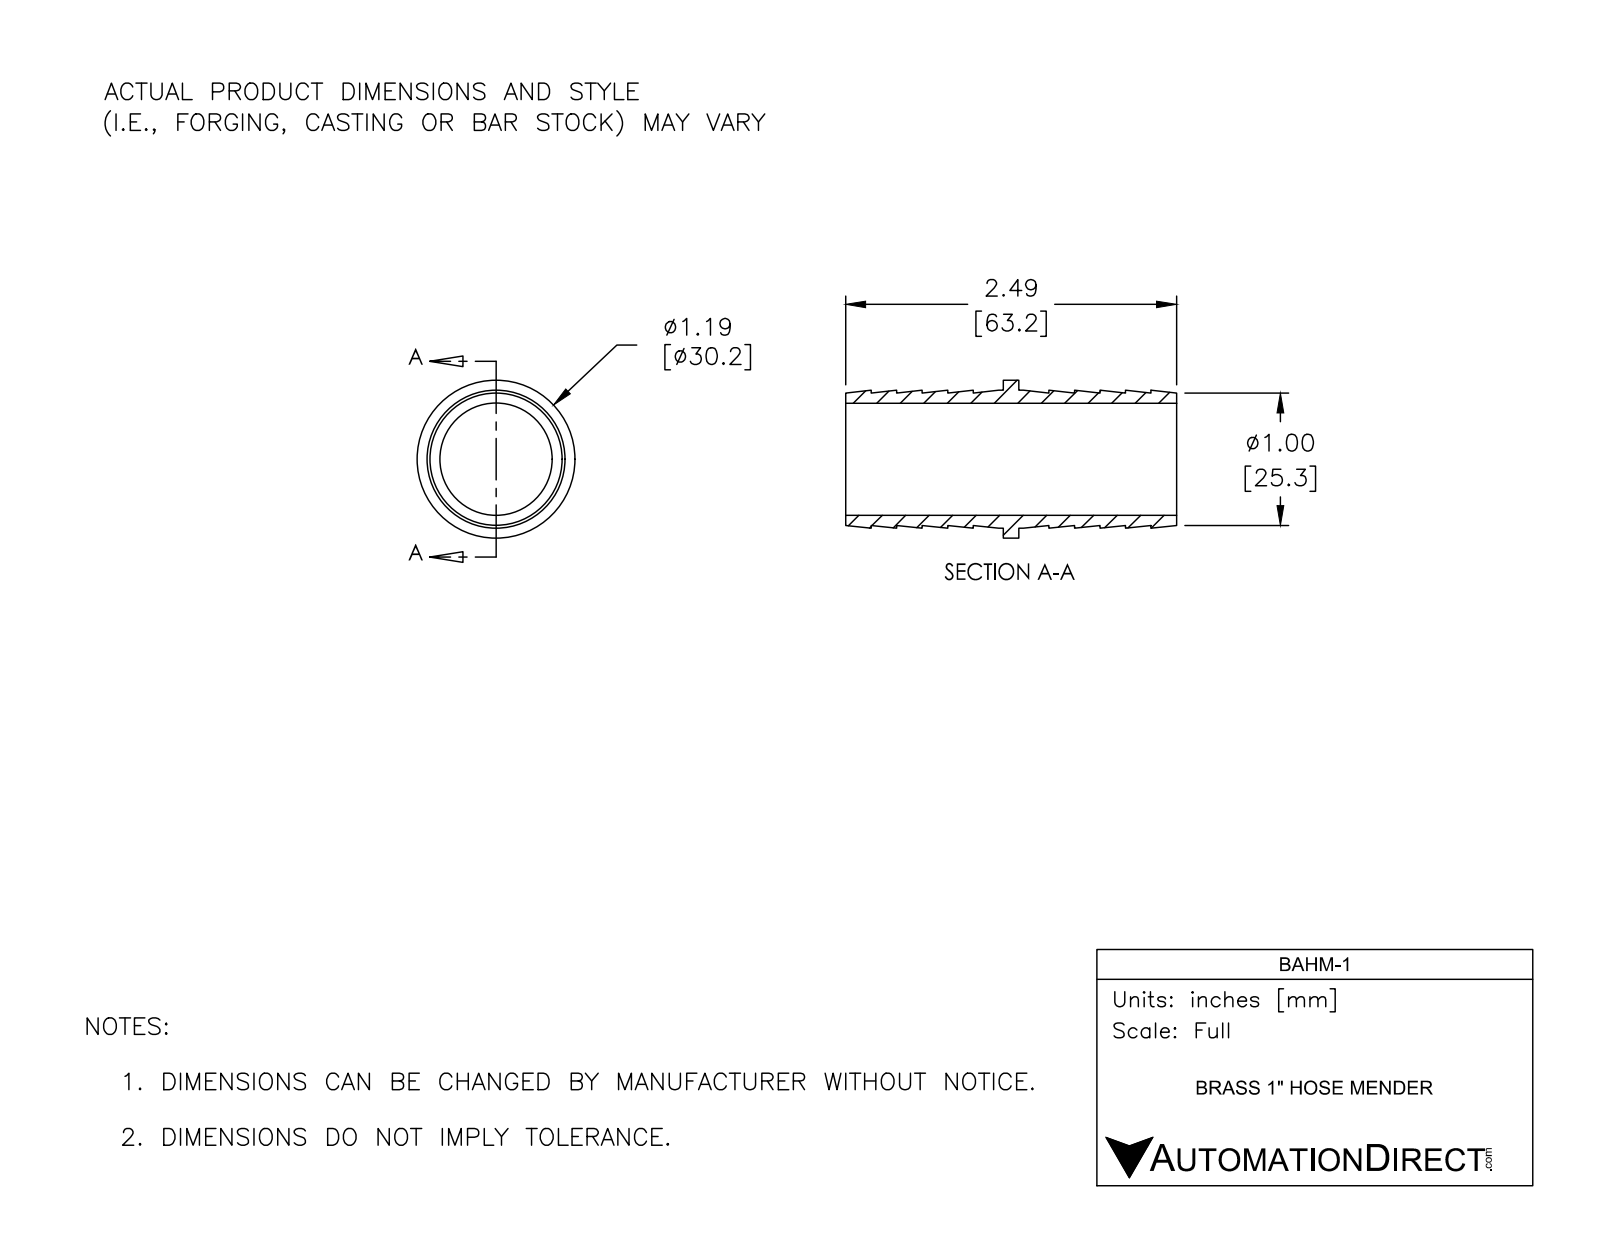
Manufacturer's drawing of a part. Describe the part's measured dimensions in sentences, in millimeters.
The part is named "BAHM-1". Its 3-D file was written by "SolidWorks 2017 (AUTOMOTIVE_DESIGN)". It is 1 solid with 46 faces: 14 planar, 8 cylindrical and 24 other. Overall it measures 63.2 by 30.1 by 30.1 millimeters. Its volume is 11 000 cubic millimeters and its surface area 10 520 square millimeters. Round holes: 1 of diameter 21.4. Round bosses or shafts: 1 of diameter 30.1, 1 of diameter 26.4. The main face-to-face distances are 30.1, 33.1, 9.8, 14.6, 4.9, 43.7, 4.9, 38.9, 34, 29.1.
